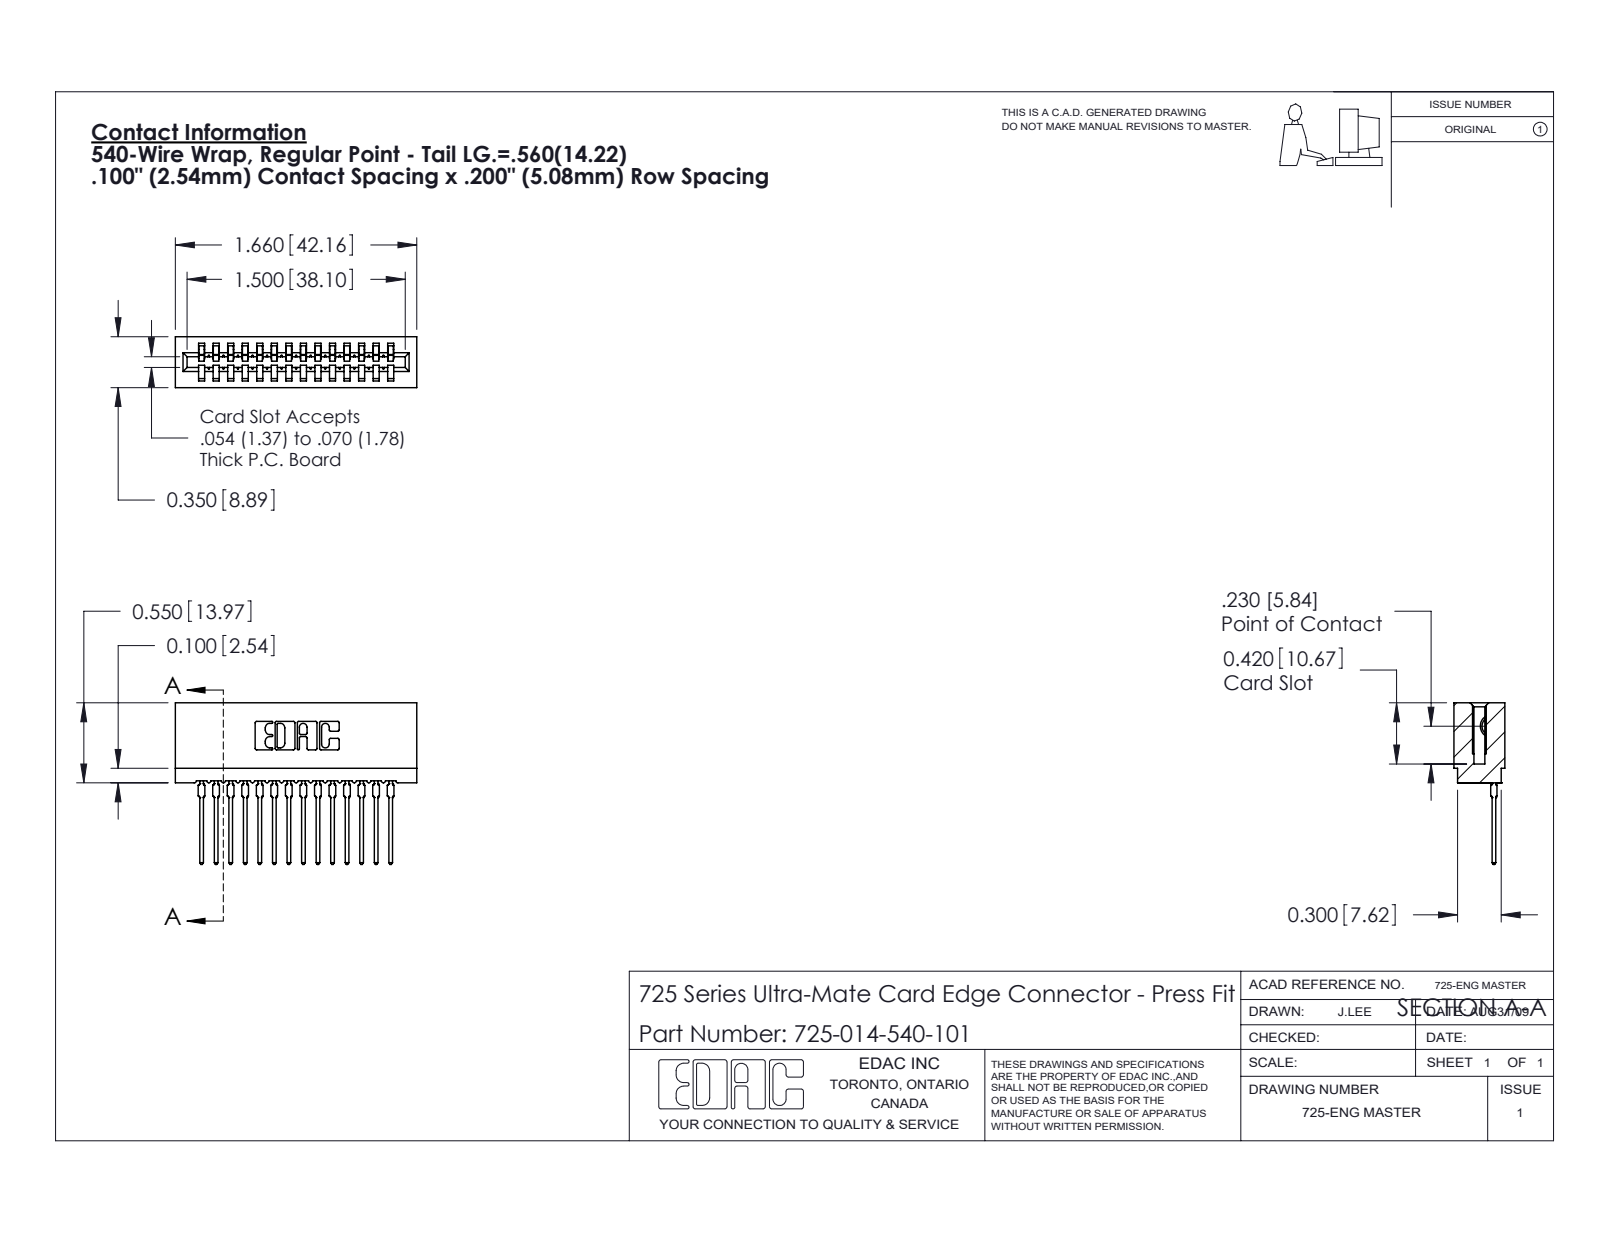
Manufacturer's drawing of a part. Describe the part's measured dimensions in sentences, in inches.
The part is named "745-292-001_540; 725-014-540-101; 725 Part_Insulator Option - 01". Its 3-D file was written by "SolidWorks 2020 (CONFIG_CONTROL_DESIGN)". It is 15 solids with 1663 faces: 993 planar, 306 cylindrical and 364 other. Overall it measures 1.66 by 1.111 by 0.35 inches. Its volume is 0.207 cubic inches and its surface area 9.561 square inches. Partial cylindrical surfaces (rounded edges, fillets, slot ends): 28 of radius 0.015, 28 of radius 0.021, 22 of radius 0.01, 6 of radius 0.007, 6 of radius 0.031, 4 of radius 0.005, 4 of radius 0.011, 3 of radius 0.026. The main face-to-face distances are 0.1, 0.2, 0.3, 0.4, 0.5, 0.35, 0.6, 0.212, 0.138, 0.7.
